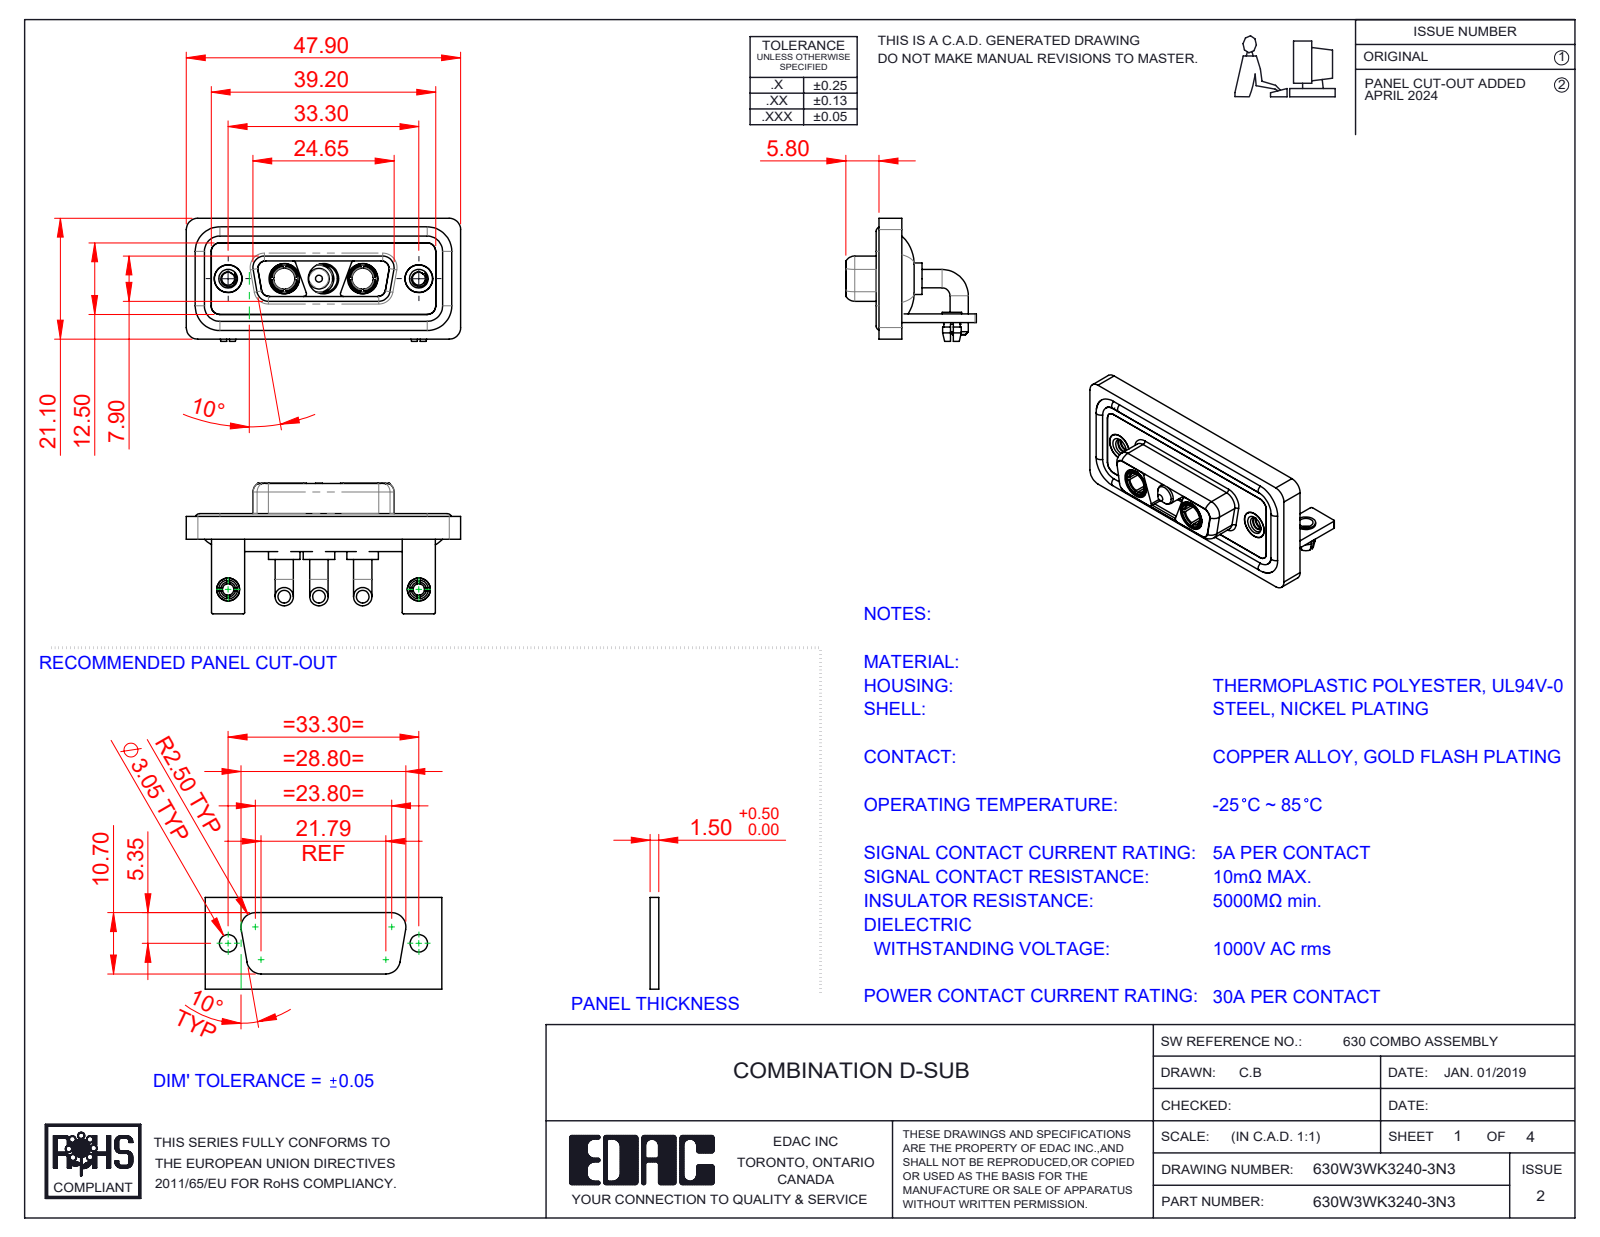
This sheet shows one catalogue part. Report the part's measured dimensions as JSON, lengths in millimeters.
{"part_name": "630Combo Board Lock_50 Contacts; 630Combo Threaded Rivet_2; 630Combo Housing_3WK3; Power Socket_30A RA (+6 more)", "step_written_by": "SolidWorks 2023 (CONFIG_CONTROL_DESIGN)", "units": "millimeters", "bodies": {"solids": 17, "faces": 735, "planar": 246, "cylindrical": 320, "other": 169}, "overall_size": [47.9, 22.8, 21.5], "volume_mm3": 6519, "surface_area_mm2": 10739, "round_holes": [[4.85, 5], [5.3, 3], [2, 2], [2.26, 2], [2.5, 2], [3.2, 2], [3.7, 2], [4, 2], [4.05, 2], [5, 2]], "round_bosses_or_shafts": [[3.2, 6], [1.6, 4], [5.5, 3], [5.2, 3], [4.75, 3], [3.75, 3], [4.96, 2], [4.95, 2]], "partial_cylinders_radius": [[2, 21], [1.5, 18], [0.25, 16], [1.35, 12], [0.5, 9], [1.6, 8], [0.6, 4], [0.65, 4]], "face_to_face_distances": [0.4, 2.9, 1.5, 3.7, 1.8, 1.1, 4.1, 1.6, 2.5, 1.4], "hole_center_spacings": [6.85, 9.8, 16.65, 23.5, 33.3, 13.7]}
